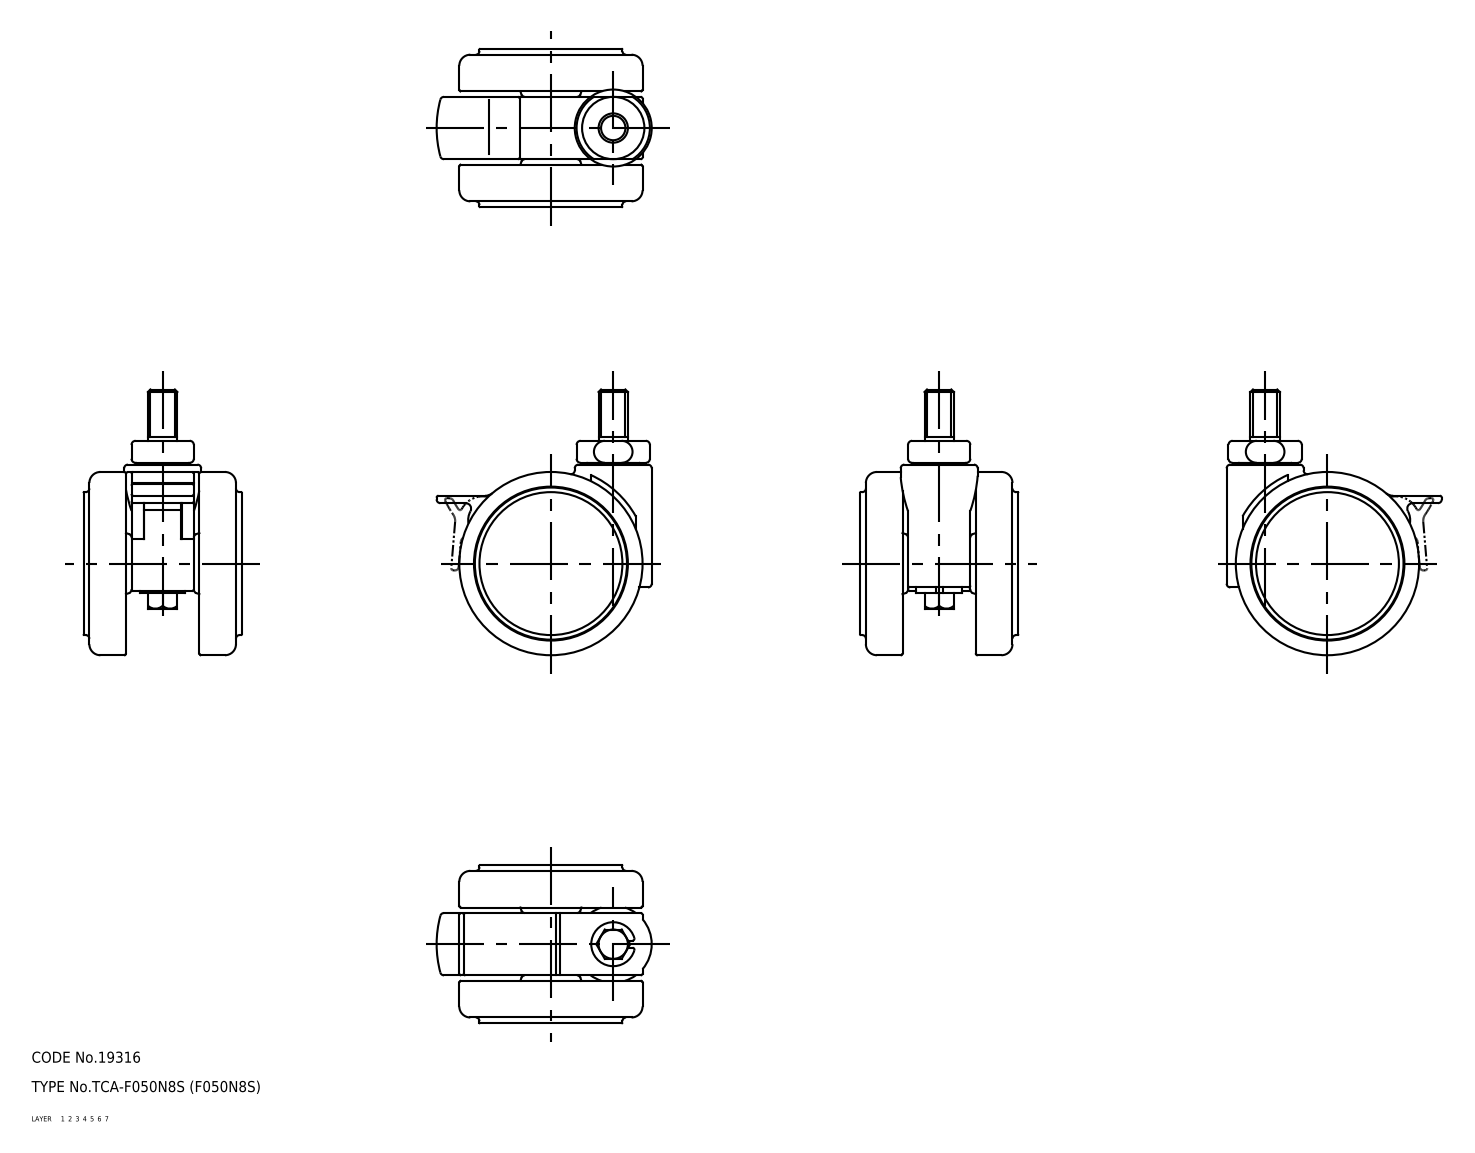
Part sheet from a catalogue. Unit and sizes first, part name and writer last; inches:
Units: inches
Overall size (bounding box): 2.854 × 2.311 × 1.701
Volume: 3.594 in³ · Surface area: 35.81 in²
Bodies: 5 solids, 246 faces (0 planar, 0 cylindrical, 246 other)
Part name (STEP PRODUCT): 67123554; 67123567; 67123580; 67123593 (+1 more)
STEP written by: CADfix (AUTOMOTIVE_DESIGN)
